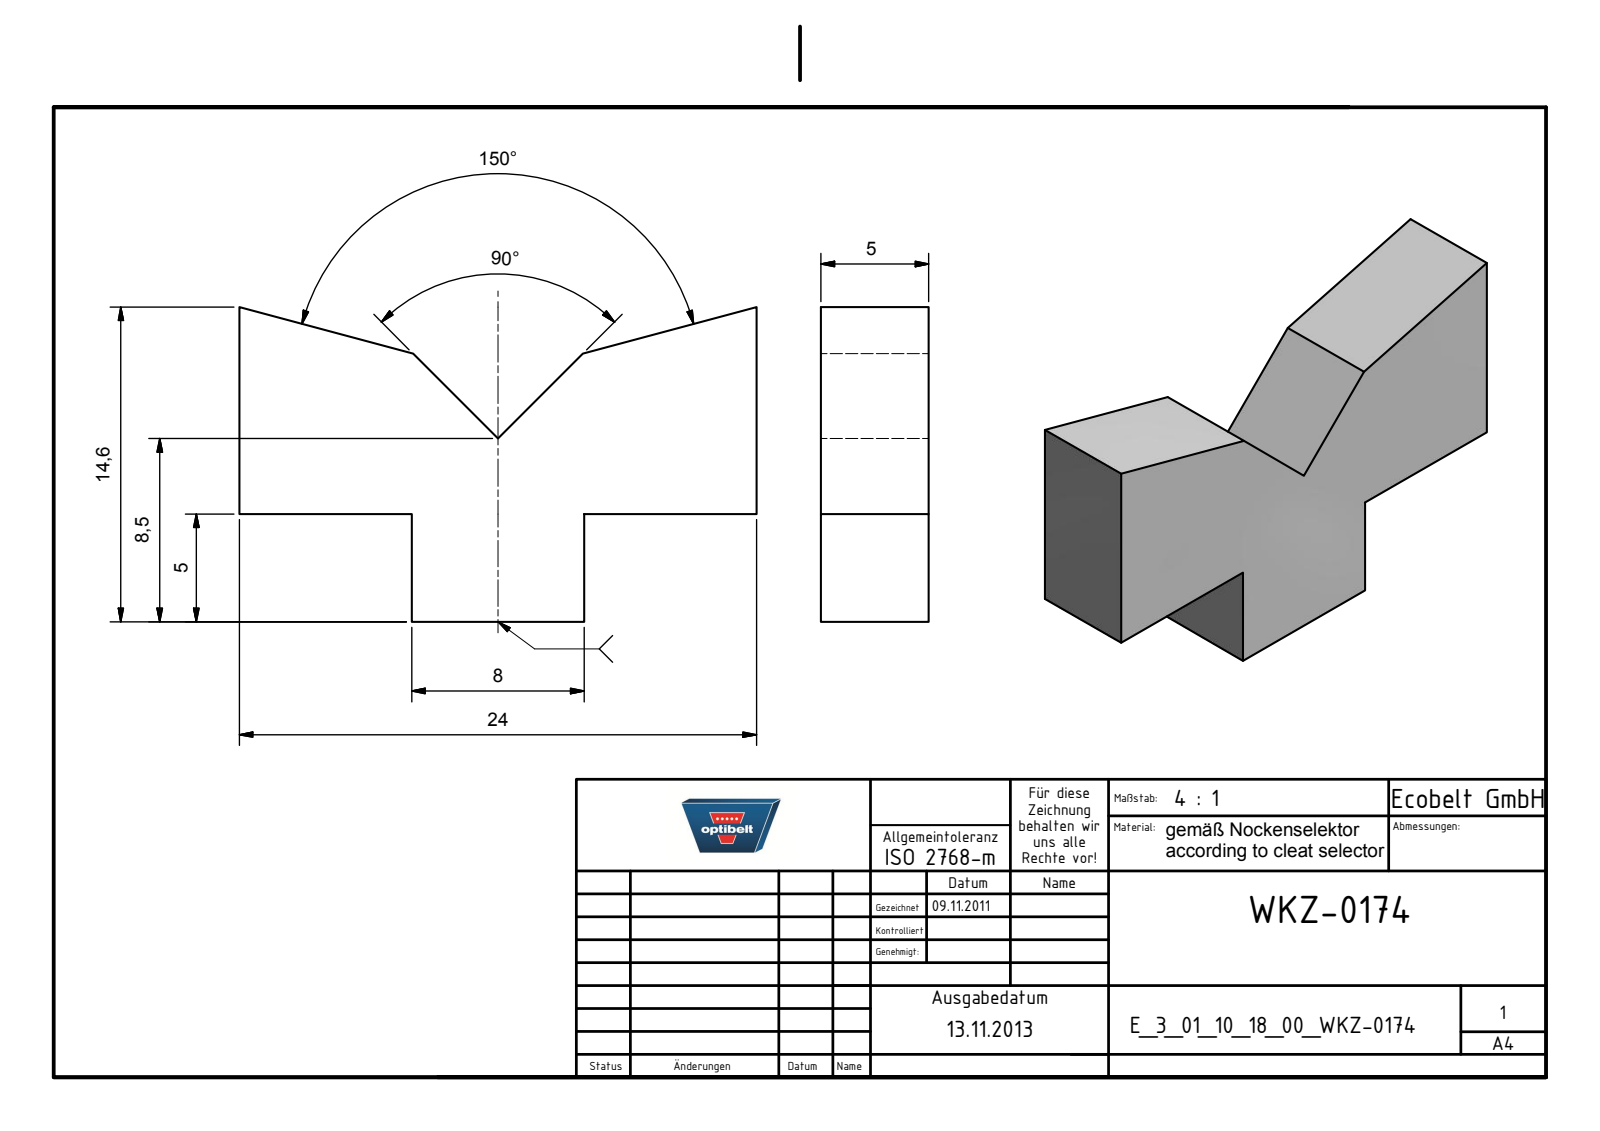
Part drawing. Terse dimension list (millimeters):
name: E_3_01_10_18_00_WKZ-0174
written by: Autodesk Inventor 2025 (AUTOMOTIVE_DESIGN)
unit: mm
bodies: 1 solid, 13 faces (13 planar, 0 cylindrical, 0 other)
size: 24 × 14.6 × 5
volume: 1 102 mm³; area: 846 mm²
face distances: 5, 8, 16, 24
